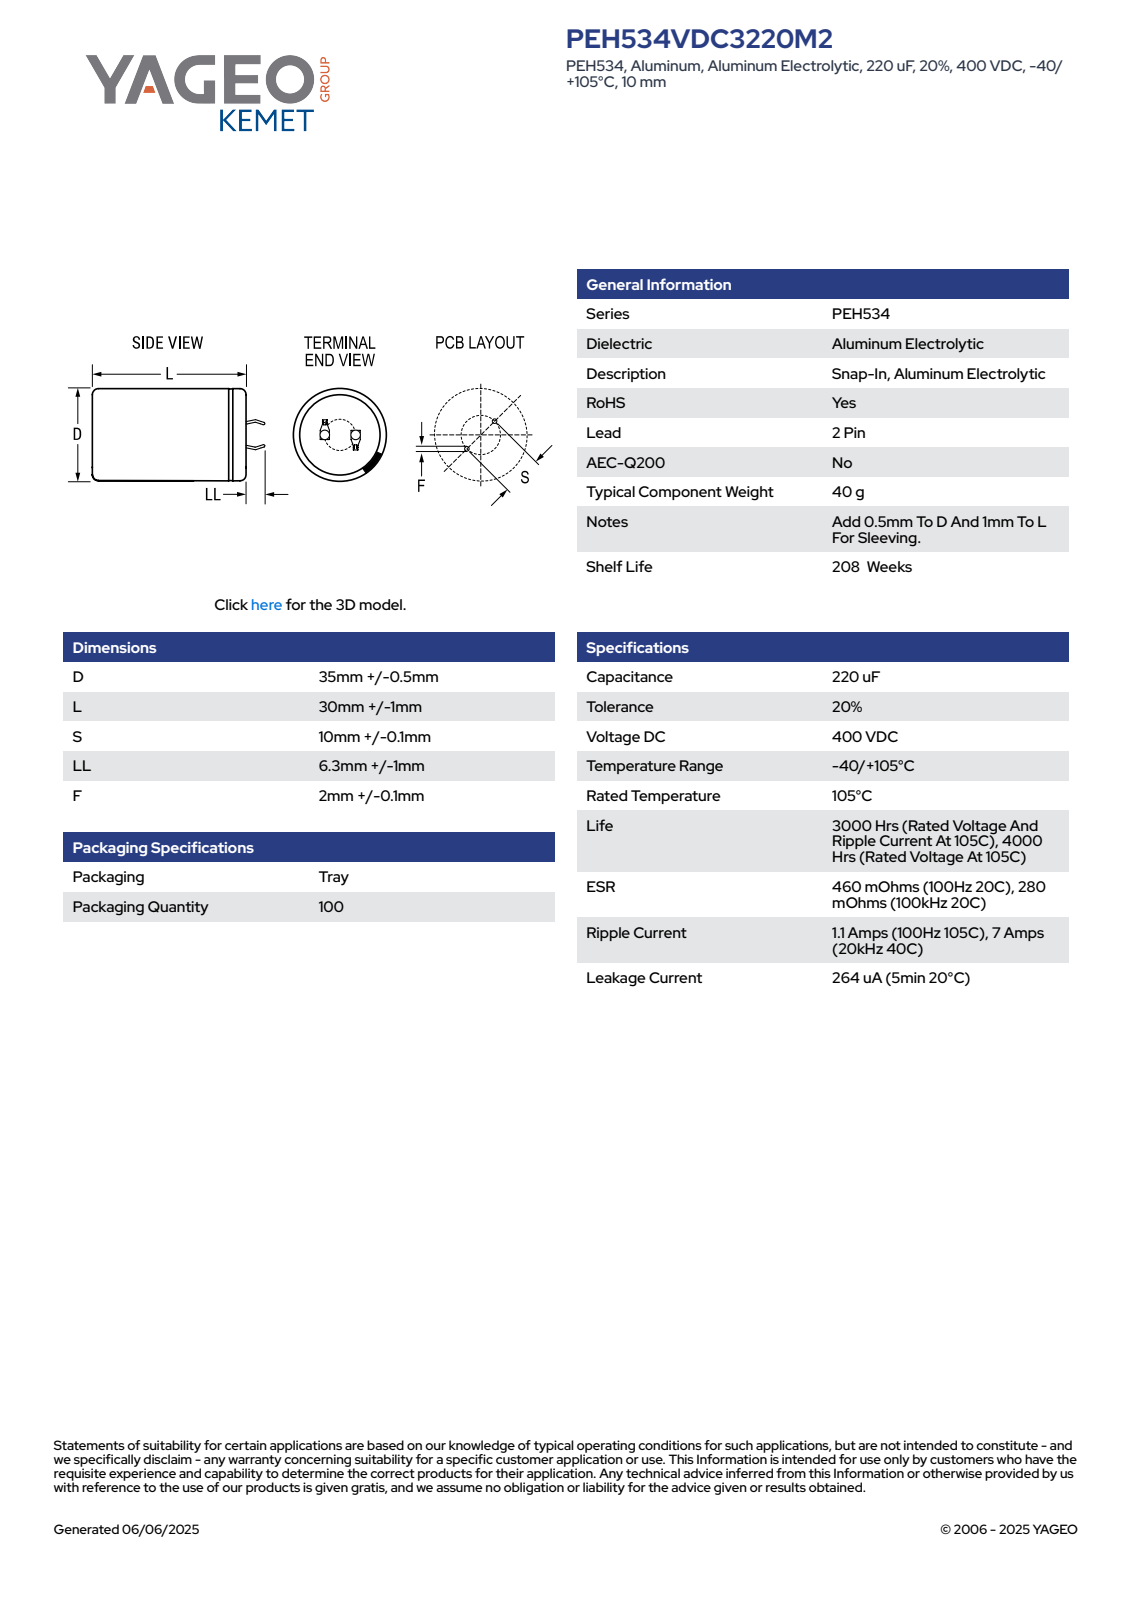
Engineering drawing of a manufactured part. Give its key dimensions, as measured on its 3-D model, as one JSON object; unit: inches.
{"part_name": "CARS_K2P_35X30_D35.5L31S10LL7.3F2.1", "step_written_by": "SolidWorks 2014 (AUTOMOTIVE_DESIGN)", "units": "inches", "bodies": {"solids": 1, "faces": 100, "planar": 52, "cylindrical": 9, "other": 39}, "overall_size": [1.507, 1.398, 1.398], "volume_in3": 1.842, "surface_area_in2": 8.426, "round_holes": [[1.237, 1]], "round_bosses_or_shafts": [[1.398, 1]], "partial_cylinders_radius": [[0.698, 1]], "face_to_face_distances": [1.22, 0.024, 1.24, 0.02, 0.279, 0.301, 0.03, 0.053, 0.302, 0.255]}
